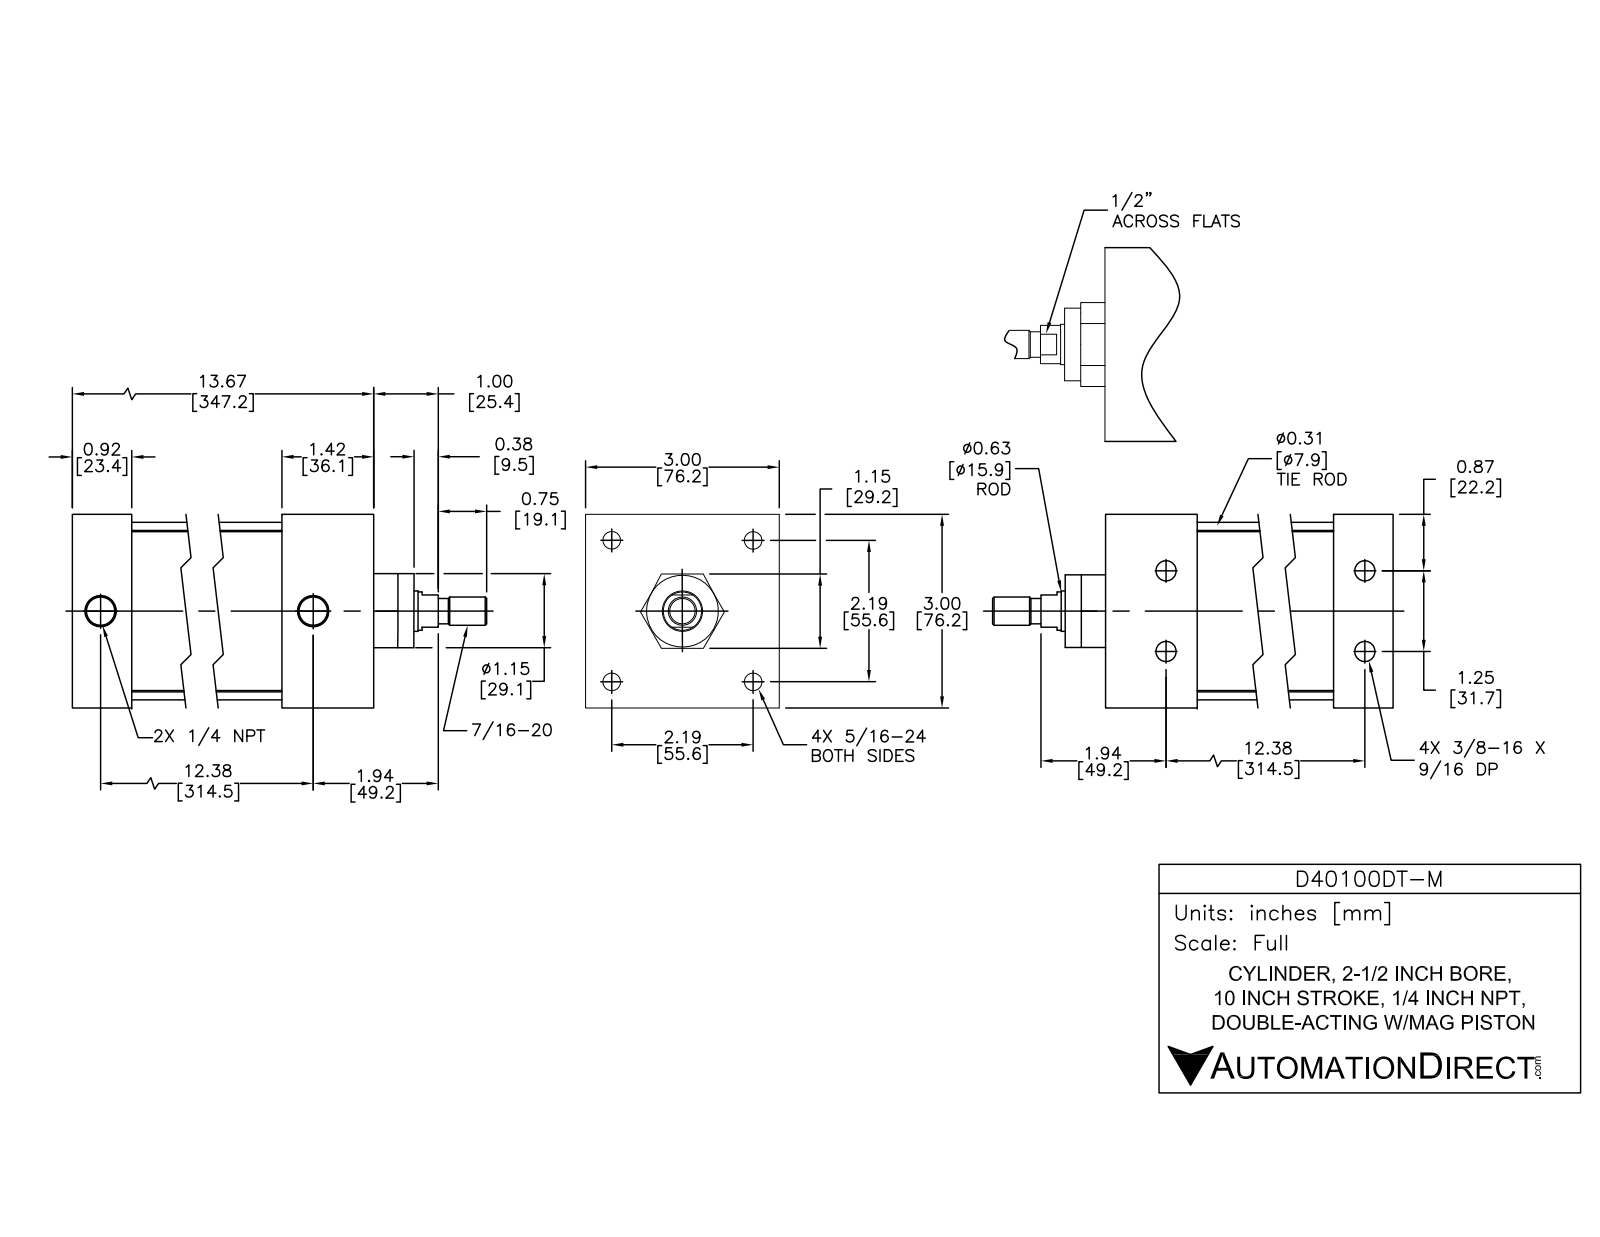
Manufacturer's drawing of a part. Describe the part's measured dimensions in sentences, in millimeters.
The part is named "D40100DT-M PISTON; D40100DT-M BODY; D40100DT-M". Its 3-D file was written by "SolidWorks 2015 (AUTOMOTIVE_DESIGN)". It is 12 solids with 298 faces: 94 planar, 114 cylindrical and 90 other. Overall it measures 393.6 by 76.2 by 76.2 millimeters. Its volume is 738 400 cubic millimeters and its surface area 240 400 square millimeters. Round holes: 4 of diameter 6.8, 4 of diameter 7.8, 4 of diameter 9.1, 4 of diameter 12.7, 2 of diameter 7.5, 2 of diameter 12.1, 1 of diameter 15.9, 1 of diameter 16, 1 of diameter 63.5. Round bosses or shafts: 4 of diameter 12.3, 4 of diameter 8, 4 of diameter 7.2, 1 of diameter 69.9, 1 of diameter 63.4, 1 of diameter 28.4, 1 of diameter 15.8, 1 of diameter 15. Partial cylindrical surfaces (rounded edges, fillets, slot ends): 4 of radius 7.6. The main face-to-face distances are 76.2, 2, 287.7, 349.1, 323.2, 25.9, 36.1, 287.2, 313.1, 25.4. The hole center spacings are 39.5, 55.9, 314.6, 314.2, 15.9, 15.9, 31.8, 79.
